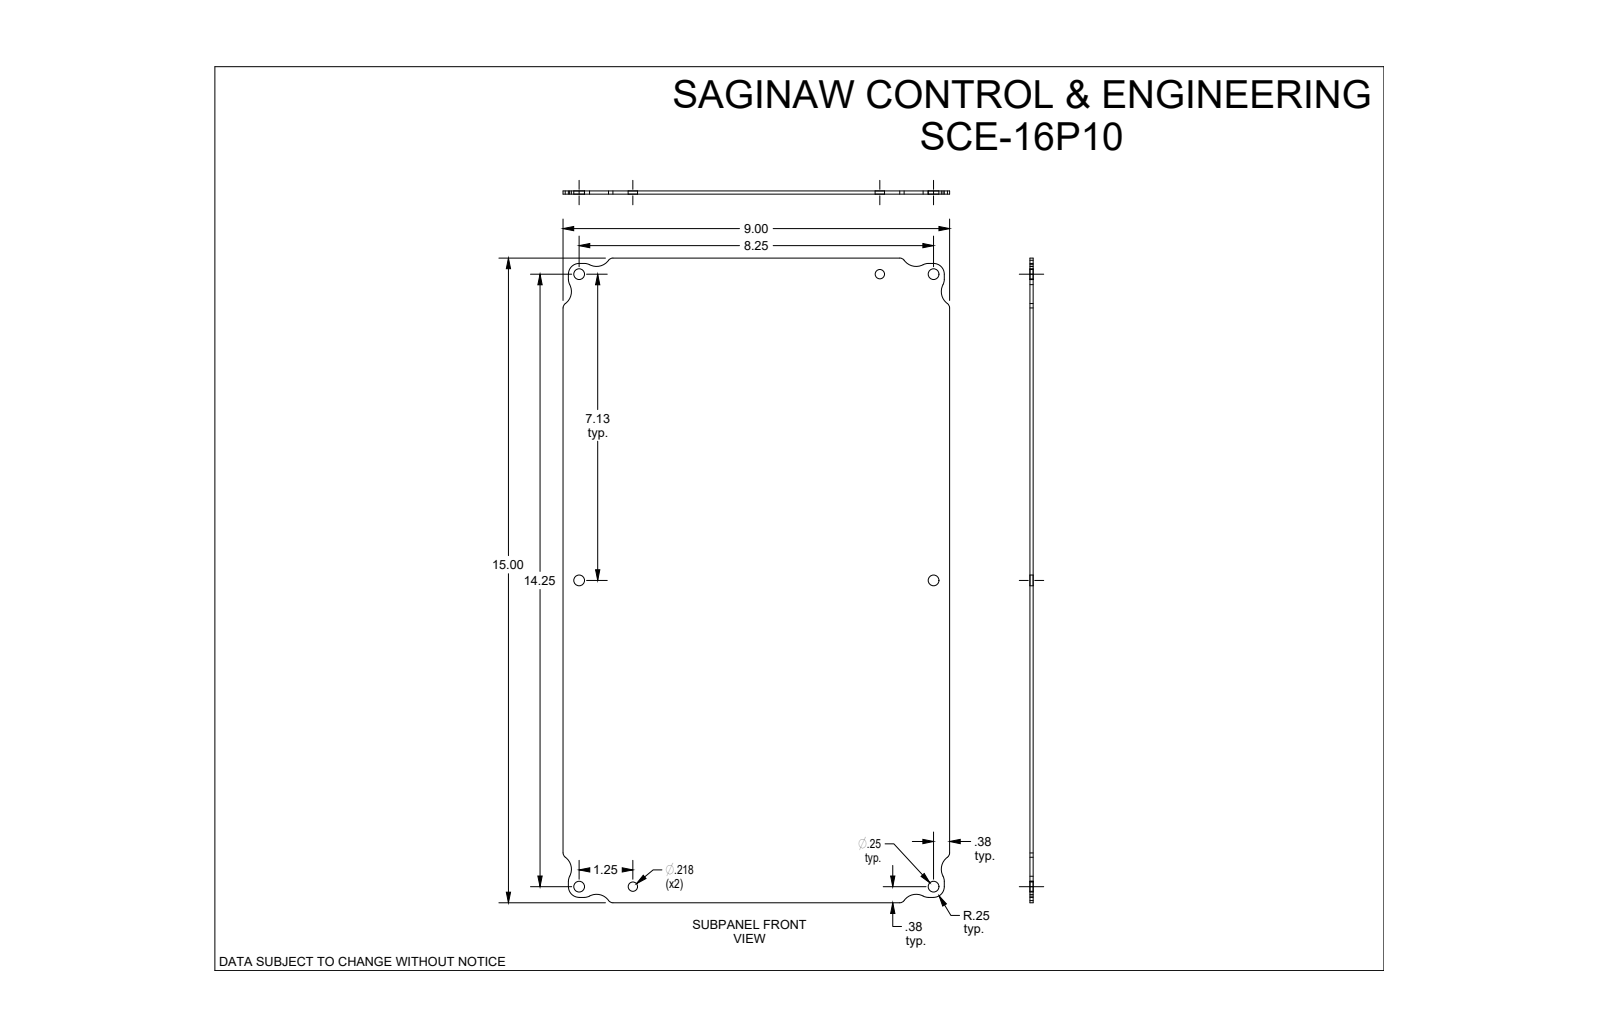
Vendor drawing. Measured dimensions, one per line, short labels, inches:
name: SCE-16P10
written by: SolidWorks 2019 (CONFIG_CONTROL_DESIGN)
unit: in
bodies: 1 solid, 50 faces (14 planar, 36 cylindrical, 0 other)
size: 15 × 9 × 0.075
volume: 10.01 in³; area: 270.8 in²
holes: 6× ⌀0.25, 2× ⌀0.218
rounds: 12× R0.25, 8× R0.125, 8× R0.344
face distances: 0.075, 9, 15, 0.125, 14.875, 0.124, 8.876, 14.75, 8.752
hole spacings: 7.125, 10.9, 8.25, 1.25, 7, 7.233, 9.988, 14.25
